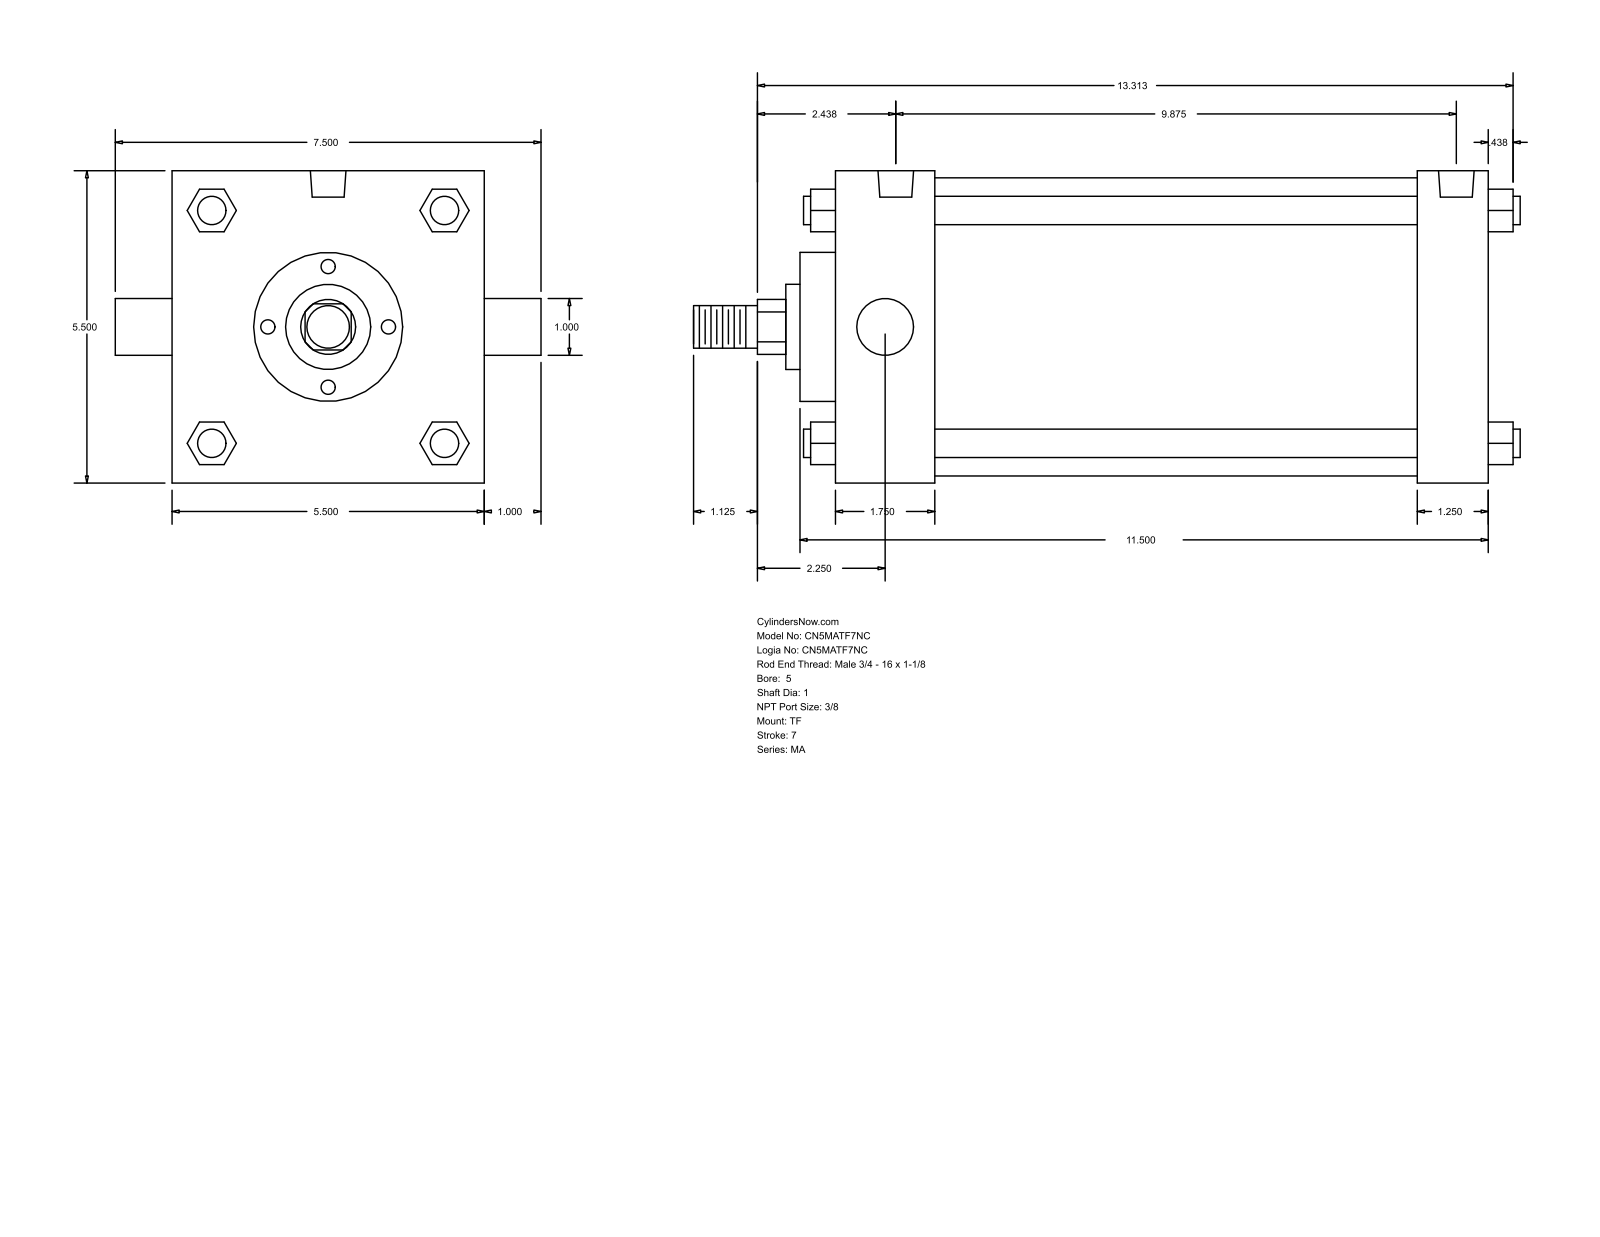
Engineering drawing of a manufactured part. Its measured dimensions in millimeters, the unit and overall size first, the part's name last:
Units: millimetres
Overall size (bounding box): 369.89 × 190.5 × 139.7
Round holes (diameter × count): ⌀11.11 ×3, ⌀15.93 ×2
Round bosses / shafts (diameter × count): ⌀12.7 ×4, ⌀25.4 ×2, ⌀133.35 ×1, ⌀66.67 ×1, ⌀38.1 ×1, ⌀19.05 ×1
Partial cylindrical surfaces — rounded edges, fillets, slot ends (radius × count): R12.29 ×1
Main face-to-face distances: 139.7, 292.1, 260.35, 31.75, 44.46, 215.89, 247.64, 15.87, 60.33, 276.22
Hole centre spacings: 4.76, 246.07, 241.31, 250.83
Bodies: 0 solids, 122 faces (93 planar, 29 cylindrical, 0 other)
Part name (STEP PRODUCT): MA_TF__0500_1
STEP written by: GSSL Pune (CONFIG_CONTROL_DESIGN)
